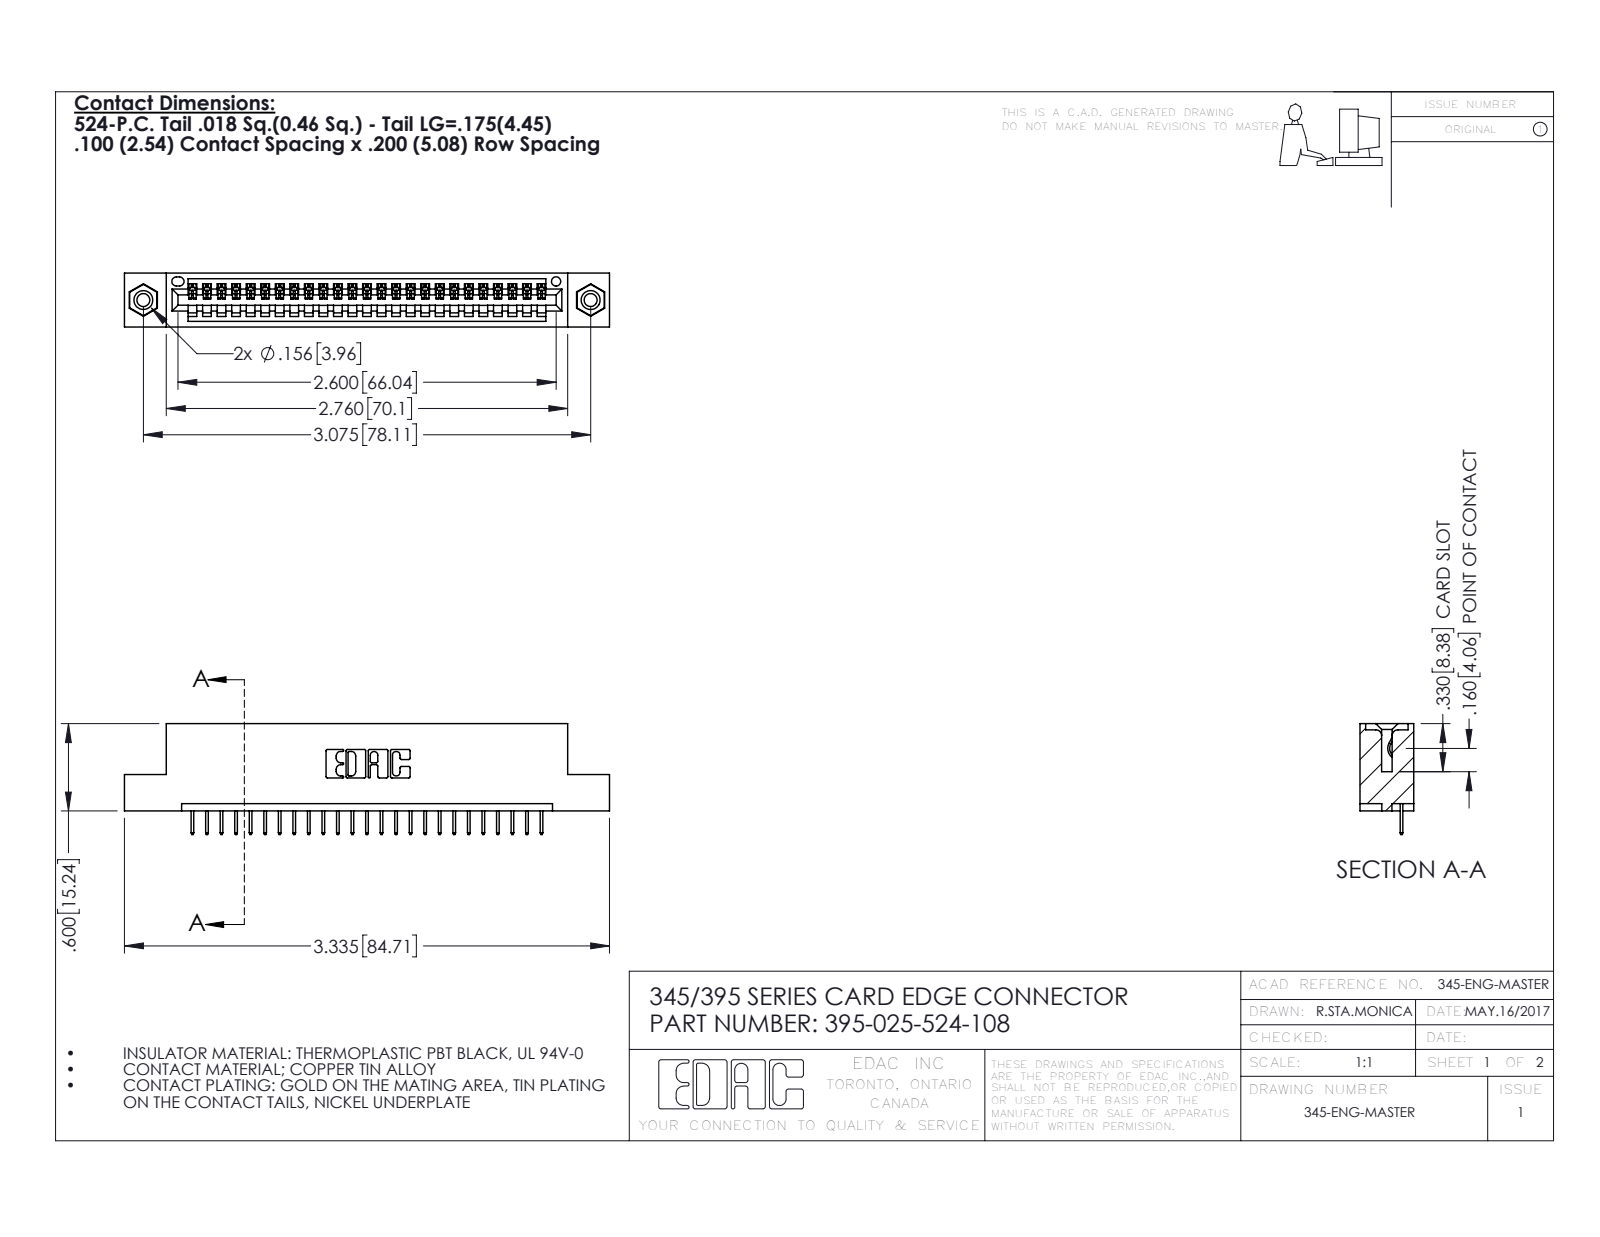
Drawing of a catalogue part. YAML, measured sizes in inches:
part_name: "345-250-001_345-250-003-102; 345-292-001_345-293-124; 395-025-524-108; 345 Part_Flush Mounting Lugs - 0.156 Dia-TI"
step_written_by: "SolidWorks 2016 (CONFIG_CONTROL_DESIGN)"
units: inches
bodies: {solids: 28, faces: 1736, planar: 1262, cylindrical: 458, other: 16}
overall_size: [3.335, 0.762, 0.37]
volume: 0.476
surface_area: 15.25
round_holes:
  - {diameter: 0.089, count: 2}
  - {diameter: 0.125, count: 2}
  - {diameter: 0.156, count: 2}
  - {diameter: 0.064, count: 1}
round_bosses_or_shafts:
  - {diameter: 0.155, count: 2}
partial_cylinders:
  - {radius: 0.006, count: 50}
  - {radius: 0.01, count: 22}
  - {radius: 0.007, count: 6}
  - {radius: 0.031, count: 6}
  - {radius: 0.026, count: 3}
  - {radius: 0.031, count: 2}
  - {radius: 0.04, count: 2}
  - {radius: 0.014, count: 1}
face_to_face_distances: [0.072, 0.298, 0.37, 0.2, 0.098, 0.272, 0.025, 0.225, 0.072, 0.149]
hole_center_spacings: [0.27, 2.84, 3.075]
